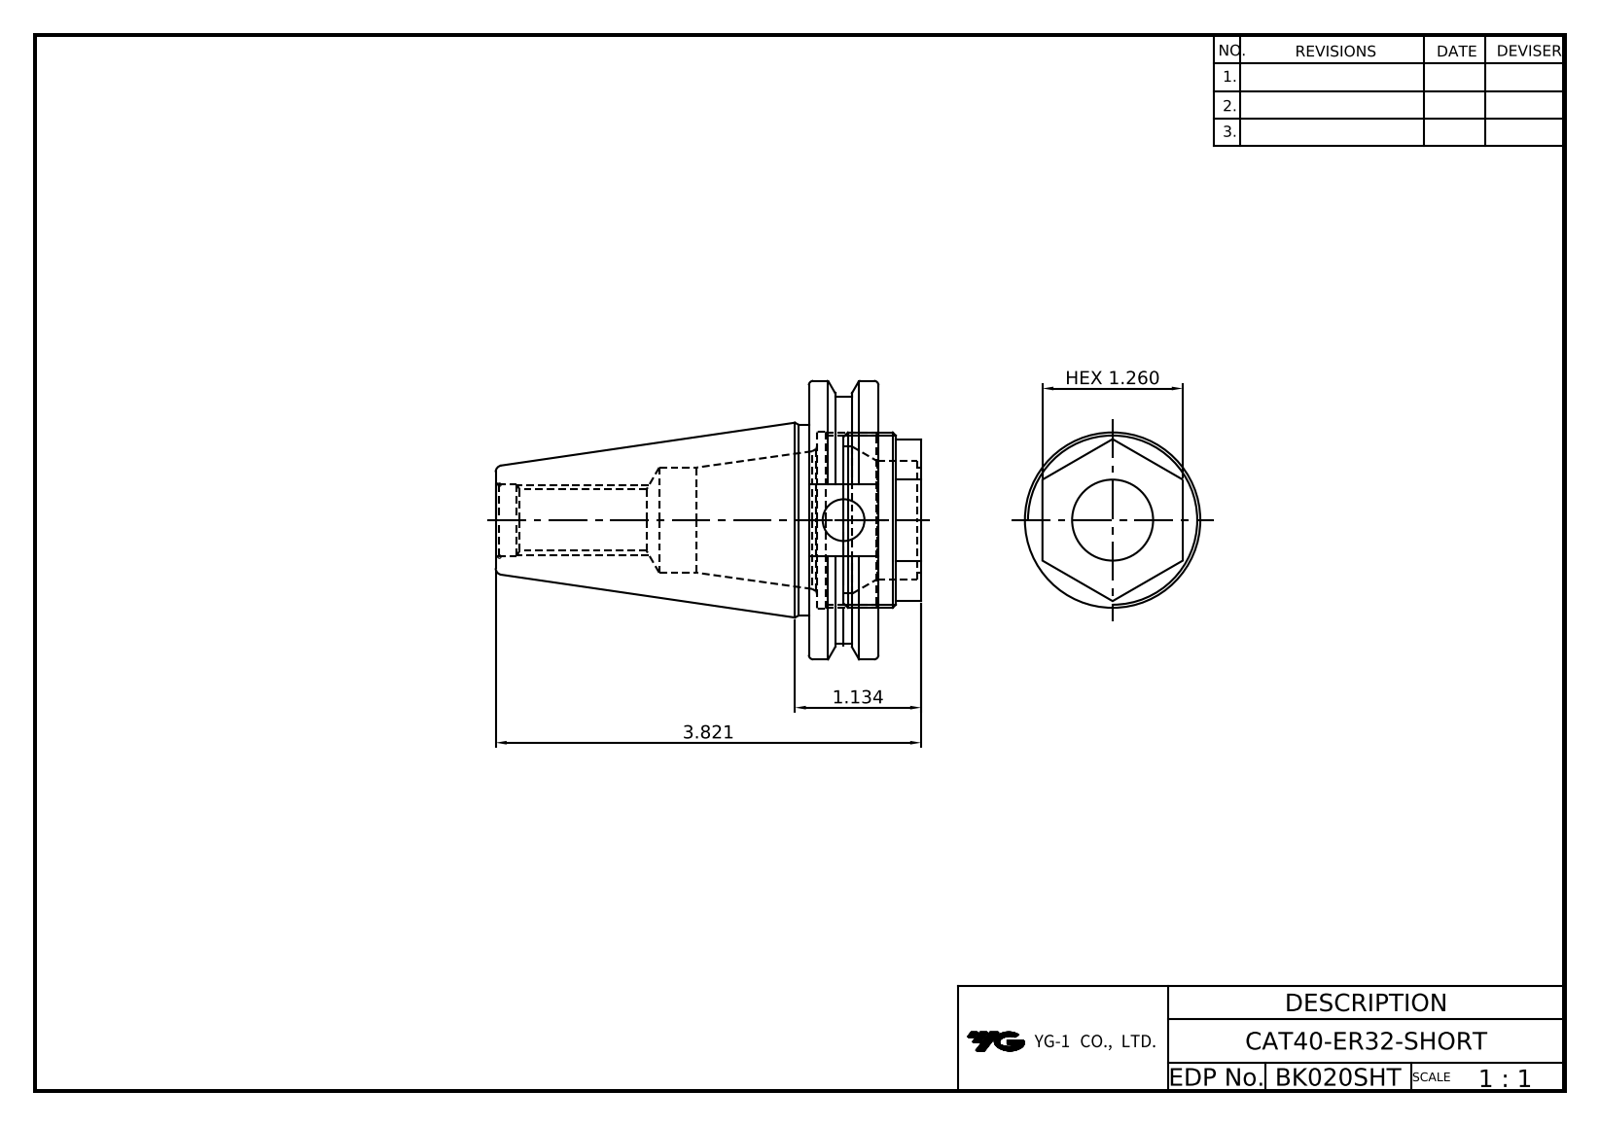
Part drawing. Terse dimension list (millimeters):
name: LO-CAT40-ER32-SHORT; ER32(SHORT TYPE)
written by: Autodesk Inventor 2025 (AUTOMOTIVE_DESIGN)
unit: mm
bodies: 2 solids, 75 faces (40 planar, 16 cylindrical, 19 other)
size: 91.1 × 63.5 × 61.09
volume: 79 147 mm³; area: 27 636 mm²
holes: 1× ⌀13.39, 1× ⌀14, 1× ⌀16.3, 1× ⌀24, 1× ⌀27, 1× ⌀38.38, 1× ⌀40.2
bosses: 1× ⌀63.5, 1× ⌀56.3, 1× ⌀43.6, 1× ⌀40
face distances: 15.88, 1.88, 14, 32.02, 19.68, 17.8, 3.8, 34.12, 36, 50
